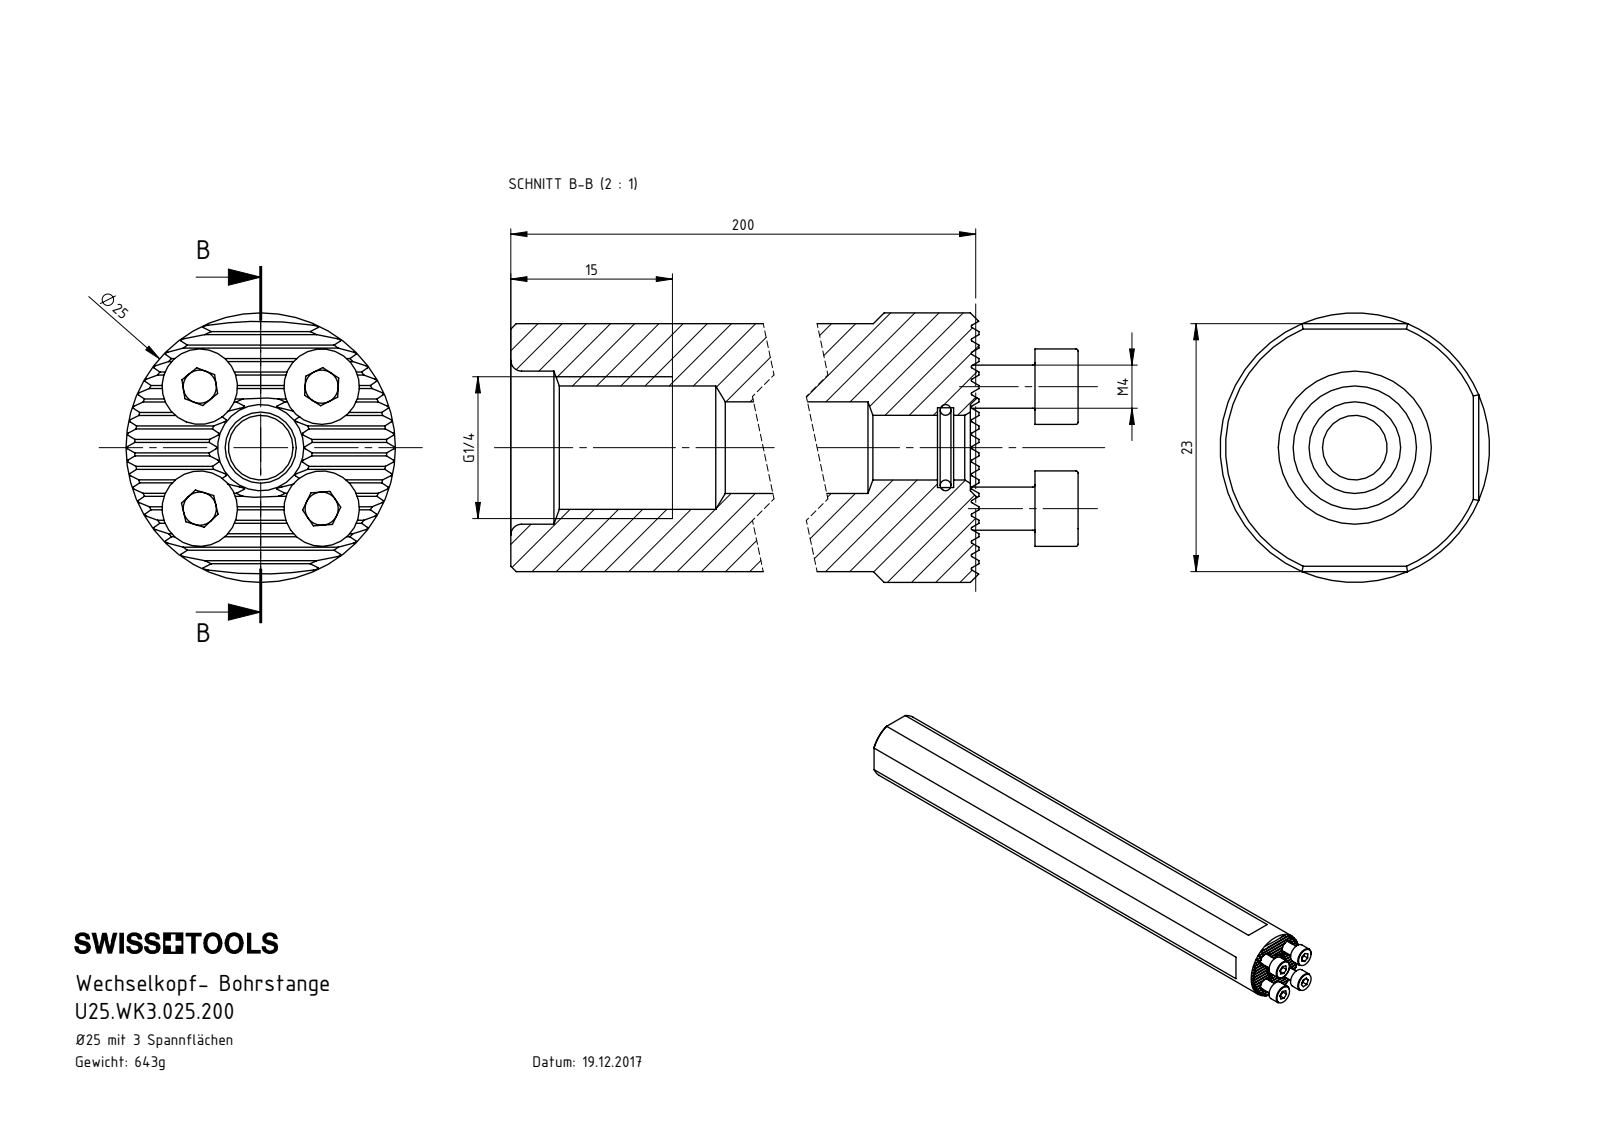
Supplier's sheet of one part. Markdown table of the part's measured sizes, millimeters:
| quantity | value |
| --- | --- |
| part name | DIN 3771 - 6x1; ISO 4762 - M4 x 12; U25.WK3.025.200; U25-WK3.025.200_A |
| STEP written by | SolidWorks 2017 (AUTOMOTIVE_DESIGN) |
| units | millimeters |
| bodies | 5 solids, 326 faces (188 planar, 76 cylindrical, 62 other) |
| overall size | 209.5 × 25 × 25 |
| volume | 82 590 mm³ |
| surface area | 23 580 mm² |
| round holes (diameter × count) | 3.3 × 4, 6 × 1, 7.4 × 1, 8.5 × 1, 11.44 × 1, 14.2 × 1 |
| round bosses / shafts (diameter × count) | 7 × 3, 4 × 3, 25 × 1 |
| partial cylindrical surfaces (radius × count) | 0.12 × 19 |
| main face-to-face distances | 23, 4.33, 1.08, 3.25, 8.66, 5.41, 7.58, 2.16, 2.17, 9.74 |
| hole center spacings | 8, 11.32, 16.01 |
